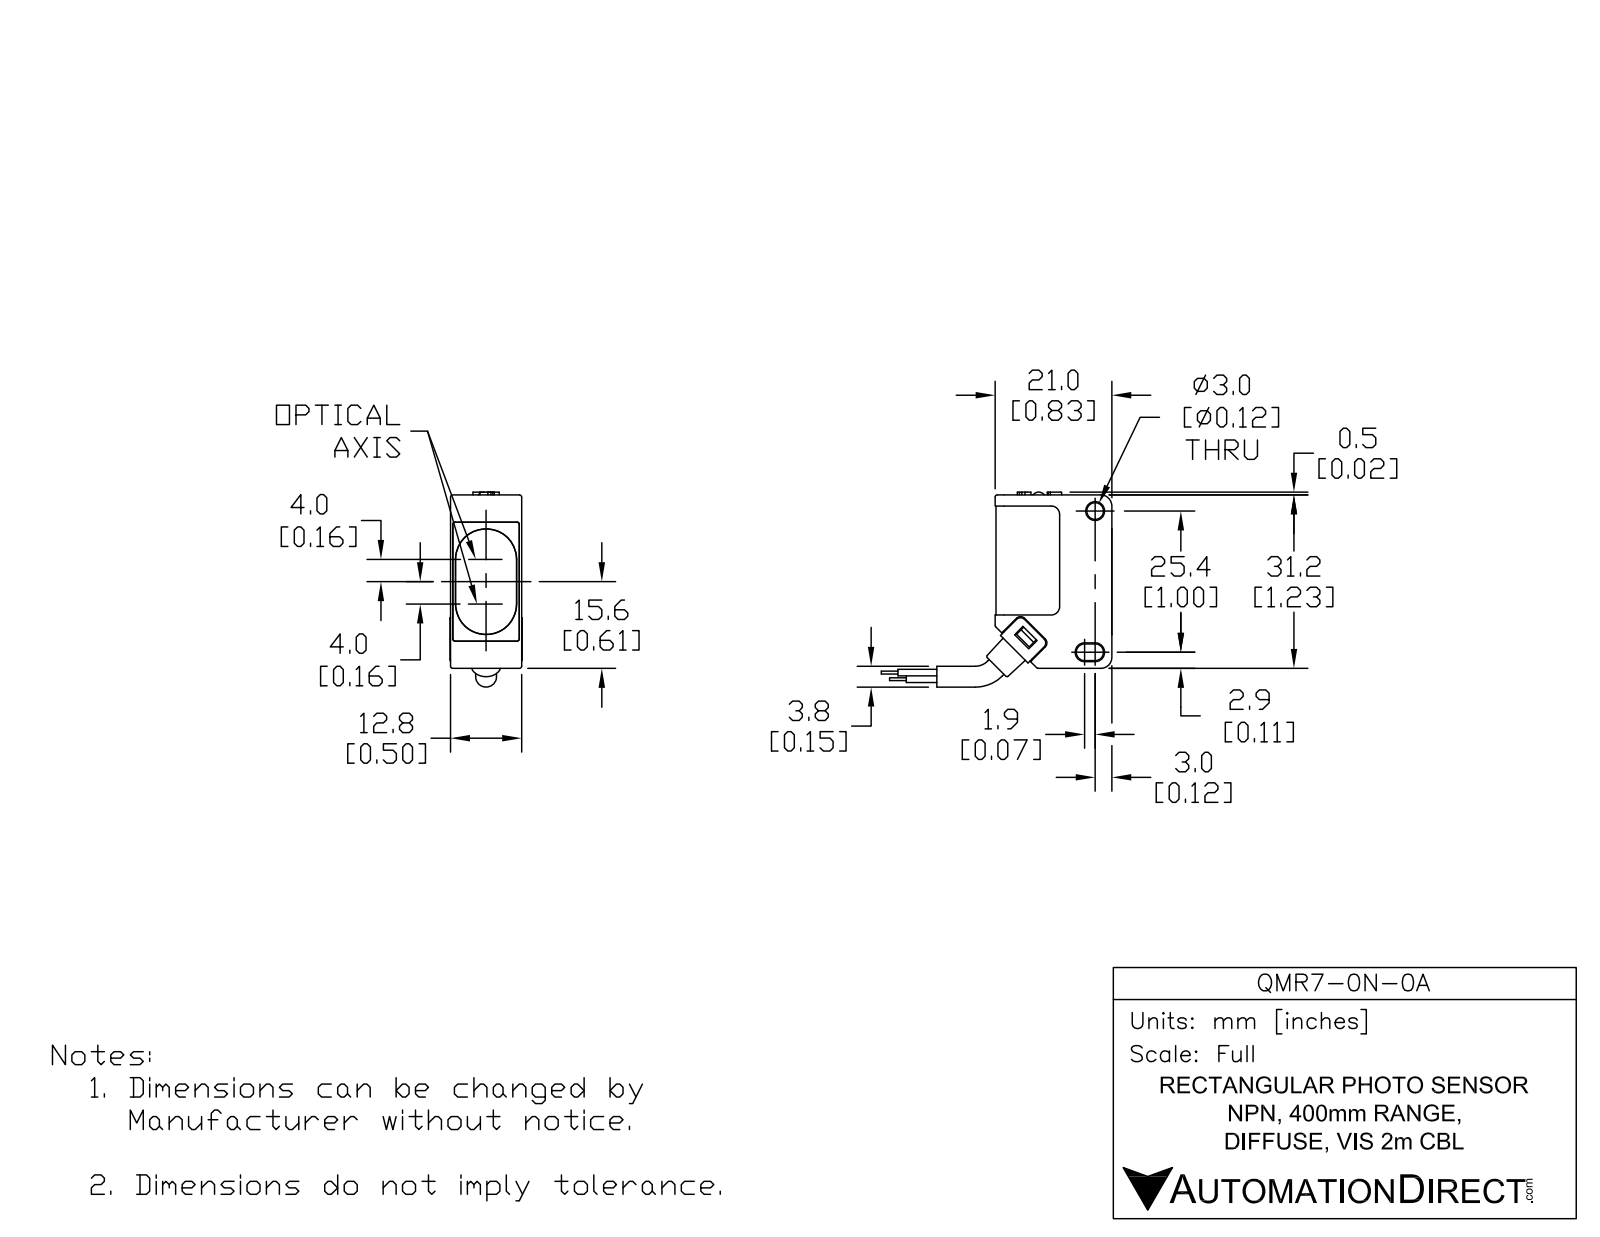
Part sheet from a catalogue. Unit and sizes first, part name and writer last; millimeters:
Units: millimetres
Overall size (bounding box): 81.1 × 26.2 × 13
Round holes (diameter × count): ⌀3 ×3, ⌀3.8 ×1, ⌀5.7 ×1, ⌀7.2 ×1
Round bosses / shafts (diameter × count): ⌀3.5 ×2
Partial cylindrical surfaces — rounded edges, fillets, slot ends (radius × count): R0.4 ×13, R0.5 ×10, R1 ×8, R1.5 ×6, R0.6 ×4, R0.2 ×2, R0.9 ×2, R1.1 ×2
Main face-to-face distances: 0.5, 12.6, 1.5, 0.4, 12.8, 3.5, 12.4, 2, 12.2, 12.5
Hole centre spacings: 5.2
Volume: 7 700 mm³ · Surface area: 5 403 mm²
Bodies: 9 solids, 258 faces (134 planar, 100 cylindrical, 24 other)
Part name (STEP PRODUCT): QMR7-0N-0A
STEP written by: SolidWorks 2017 (AUTOMOTIVE_DESIGN)
